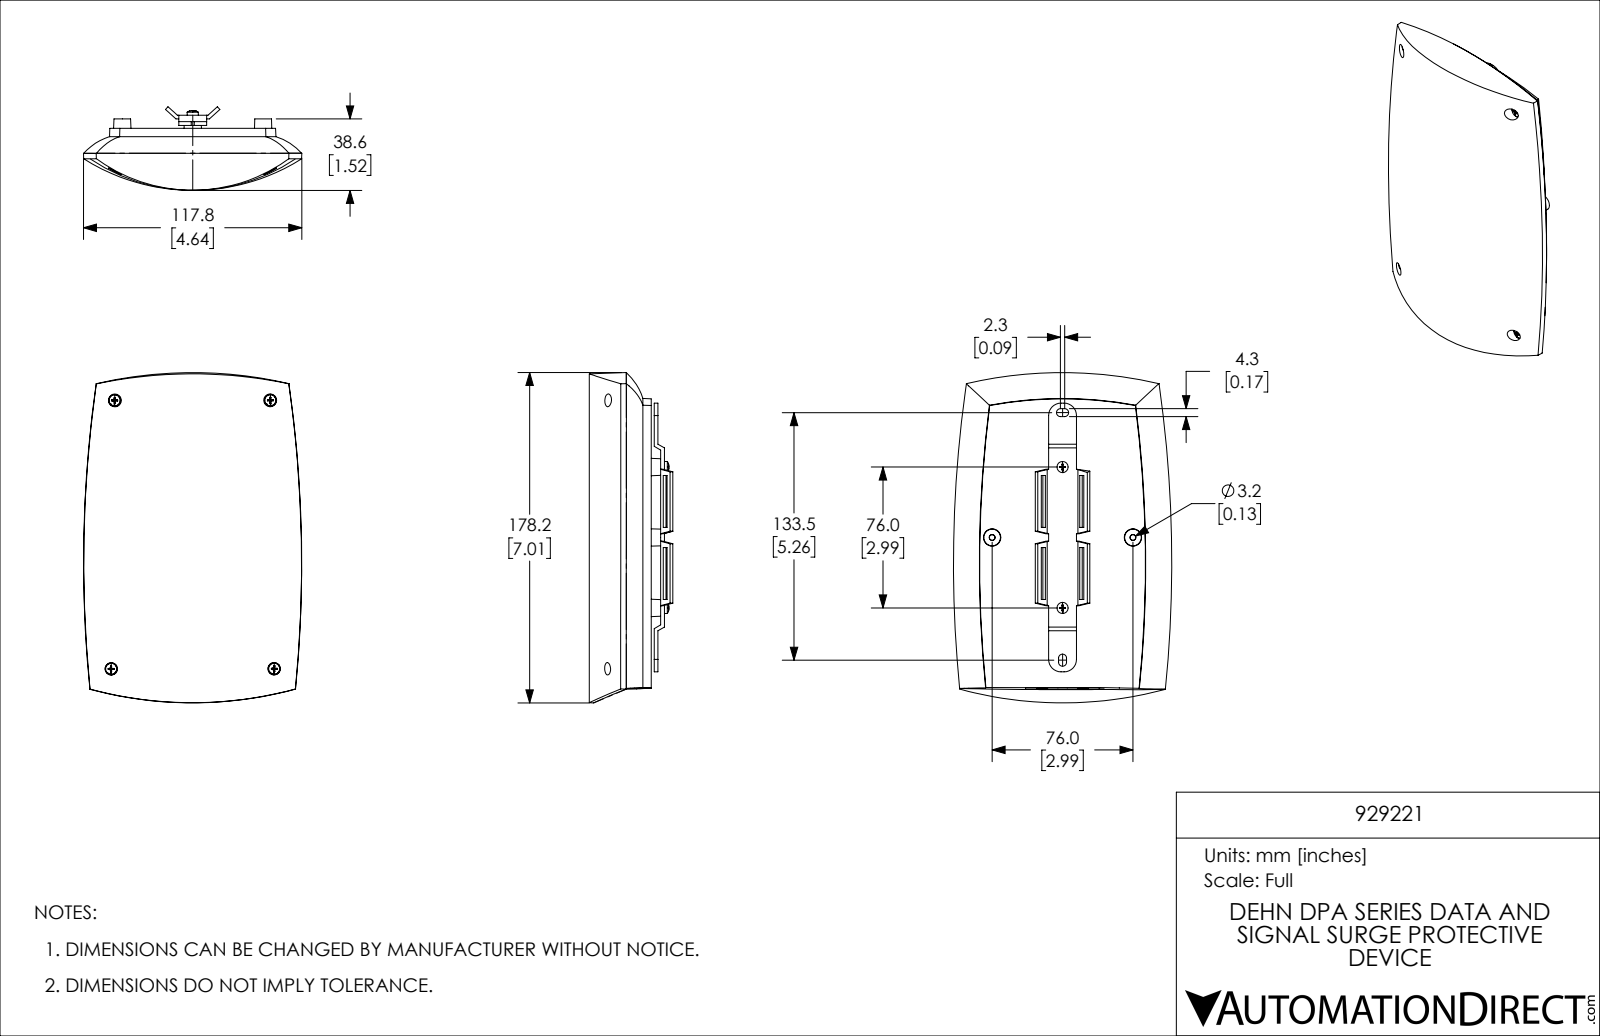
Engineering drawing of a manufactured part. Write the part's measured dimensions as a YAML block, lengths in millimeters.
part_name: "929221"
step_written_by: "SolidWorks 2019 (CONFIG_CONTROL_DESIGN)"
units: millimeters
bodies: {solids: 1, faces: 239, planar: 149, cylindrical: 25, other: 65}
overall_size: [178.2, 117.8, 45.1]
volume: 498700
surface_area: 57050
round_holes:
  - {diameter: 6, count: 2}
round_bosses_or_shafts:
  - {diameter: 6, count: 6}
partial_cylinders:
  - {radius: 2.2, count: 4}
  - {radius: 6.7, count: 4}
face_to_face_distances: [2, 5.1, 7.1, 3.5, 5.5, 1.6, 1.5, 3.6, 3, 2.5]
hole_center_spacings: [22]
